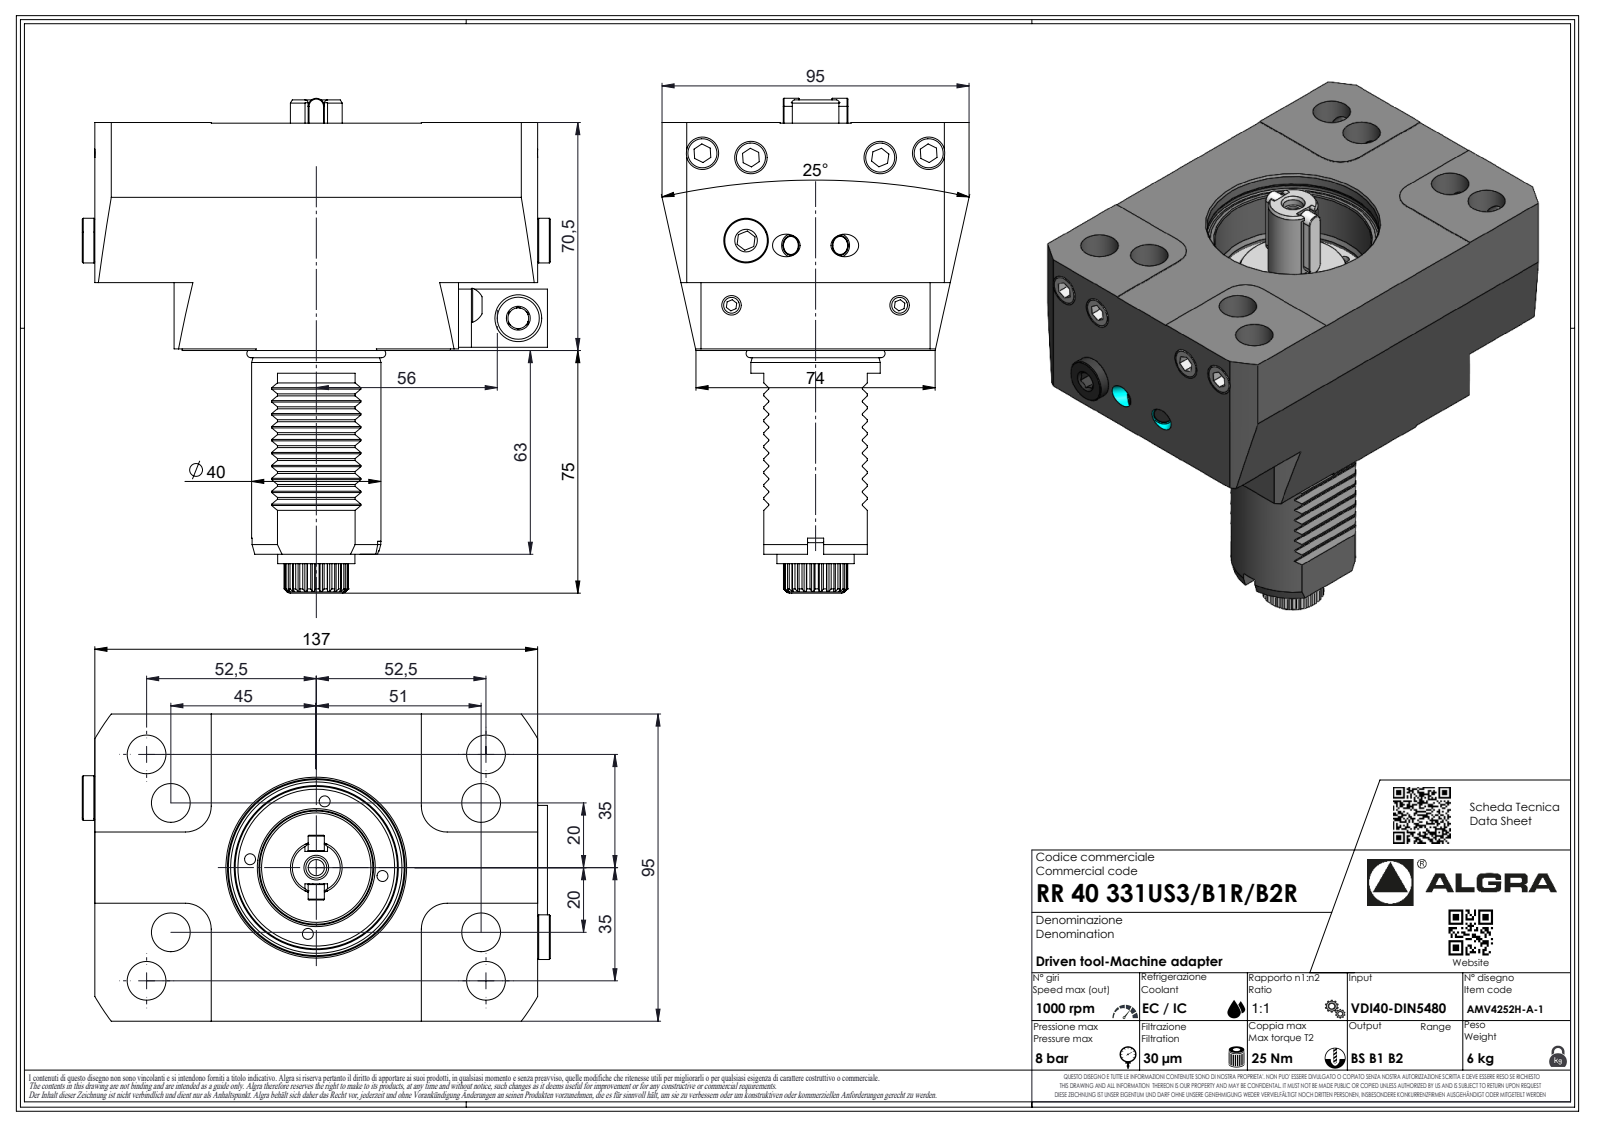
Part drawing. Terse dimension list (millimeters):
name: RR40331US3B1RB2R
written by: SolidWorks 2023 (AUTOMOTIVE_DESIGN)
unit: mm
bodies: 1 solid, 642 faces (398 planar, 99 cylindrical, 145 other)
size: 152.5 × 137 × 95
volume: 839 535 mm³; area: 62 944 mm²
holes: 1× ⌀2.1
bosses: 1× ⌀40, 1× ⌀38.7, 1× ⌀23.9, 1× ⌀16, 1× ⌀6.37, 1× ⌀1.7
rounds: 20× R0.3, 7× R0.33, 7× R0.52, 7× R3.7, 4× R3, 1× R0.21, 1× R9.92, 1× R12.95
face distances: 49.5, 137, 21, 70.5, 24.5, 112.5, 95, 2.83, 63.5, 88
